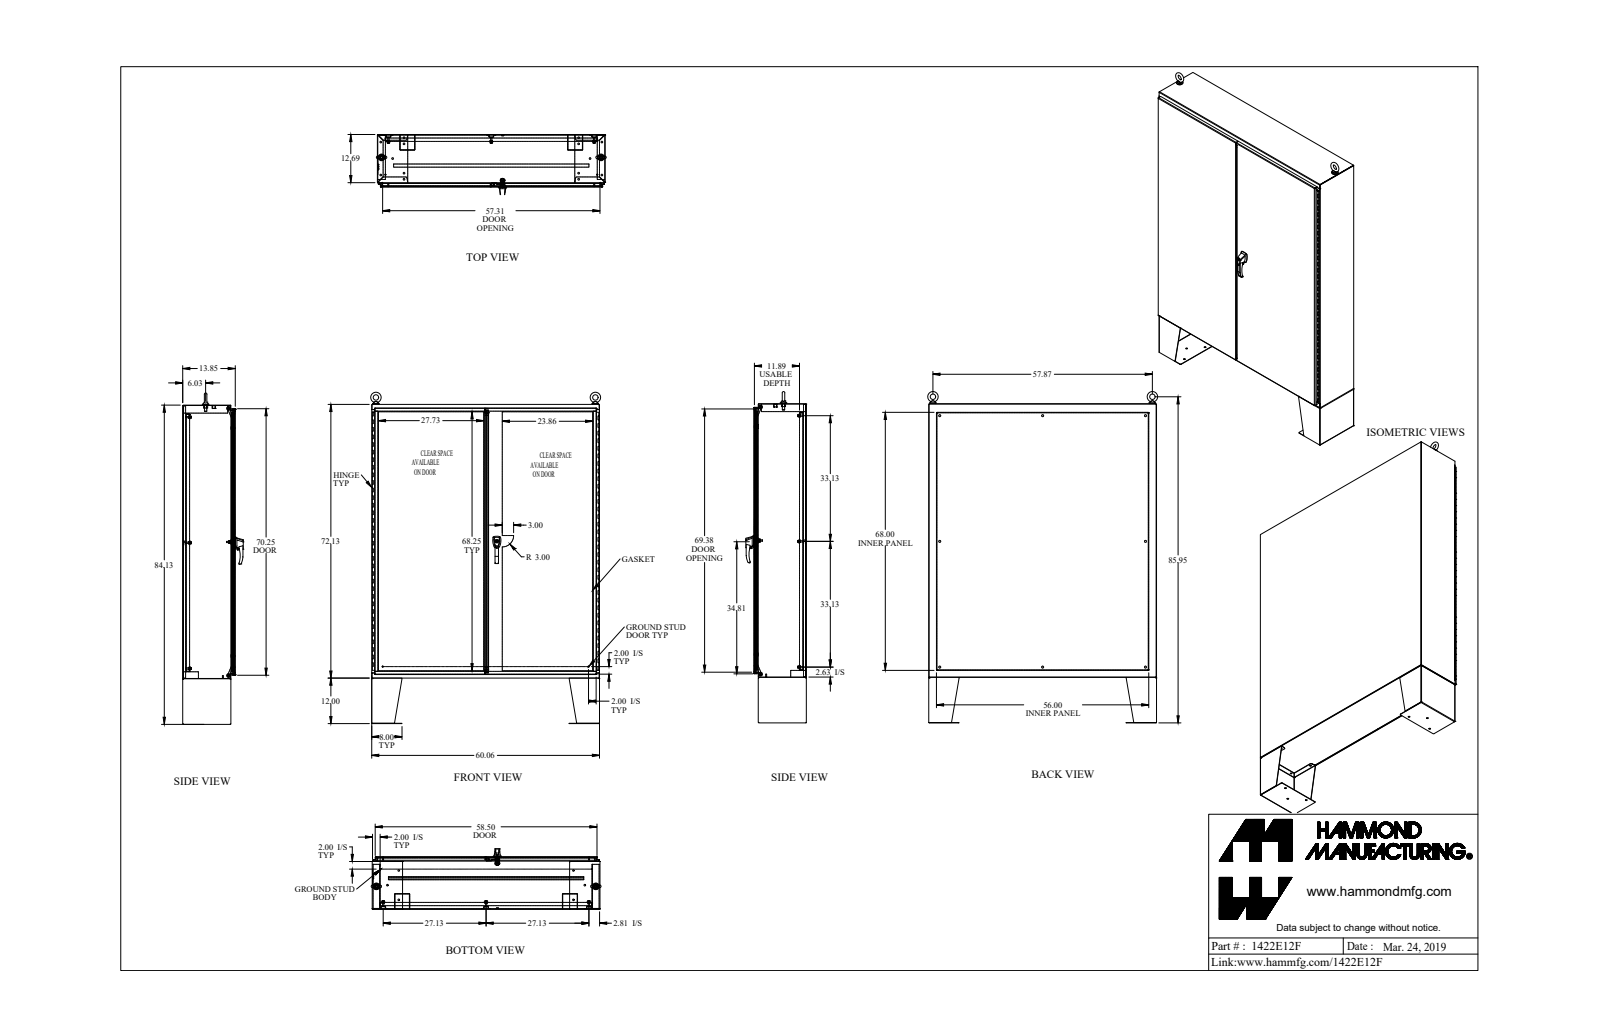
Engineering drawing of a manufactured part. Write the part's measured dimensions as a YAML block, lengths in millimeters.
part_name: "1422E12F_Default"
step_written_by: "SolidWorks 2019 (CONFIG_CONTROL_DESIGN)"
units: millimeters
bodies: {solids: 92, faces: 2997, planar: 1372, cylindrical: 1378, other: 247}
overall_size: [2229.6, 1552.5, 405.5]
volume: 34360000
surface_area: 25170000
round_holes:
  - {diameter: 7.7, count: 24}
  - {diameter: 11.1, count: 14}
  - {diameter: 7.8, count: 9}
  - {diameter: 14.3, count: 8}
  - {diameter: 11.3, count: 6}
  - {diameter: 2.8, count: 2}
  - {diameter: 6.4, count: 2}
  - {diameter: 6.5, count: 2}
  - {diameter: 7.1, count: 2}
  - {diameter: 7.1, count: 2}
  - {diameter: 8, count: 2}
  - {diameter: 9.9, count: 2}
round_bosses_or_shafts:
  - {diameter: 25.4, count: 10}
  - {diameter: 16.5, count: 8}
  - {diameter: 9.5, count: 8}
  - {diameter: 8.4, count: 8}
  - {diameter: 7.1, count: 6}
  - {diameter: 6.4, count: 4}
  - {diameter: 44.5, count: 2}
  - {diameter: 38.1, count: 2}
partial_cylinders:
  - {radius: 1.2, count: 32}
  - {radius: 3.6, count: 32}
  - {radius: 3.2, count: 22}
  - {radius: 0.5, count: 16}
  - {radius: 1.5, count: 14}
  - {radius: 2.9, count: 12}
  - {radius: 4.7, count: 9}
  - {radius: 1.3, count: 8}
face_to_face_distances: [2.4, 3.2, 349.3, 346.2, 348.6, 351.7, 3.2, 42.8, 305.7, 303.3]
hole_center_spacings: [152.4, 304.8, 1491, 1514.2, 457.2, 1552, 609.6, 1603.6]
